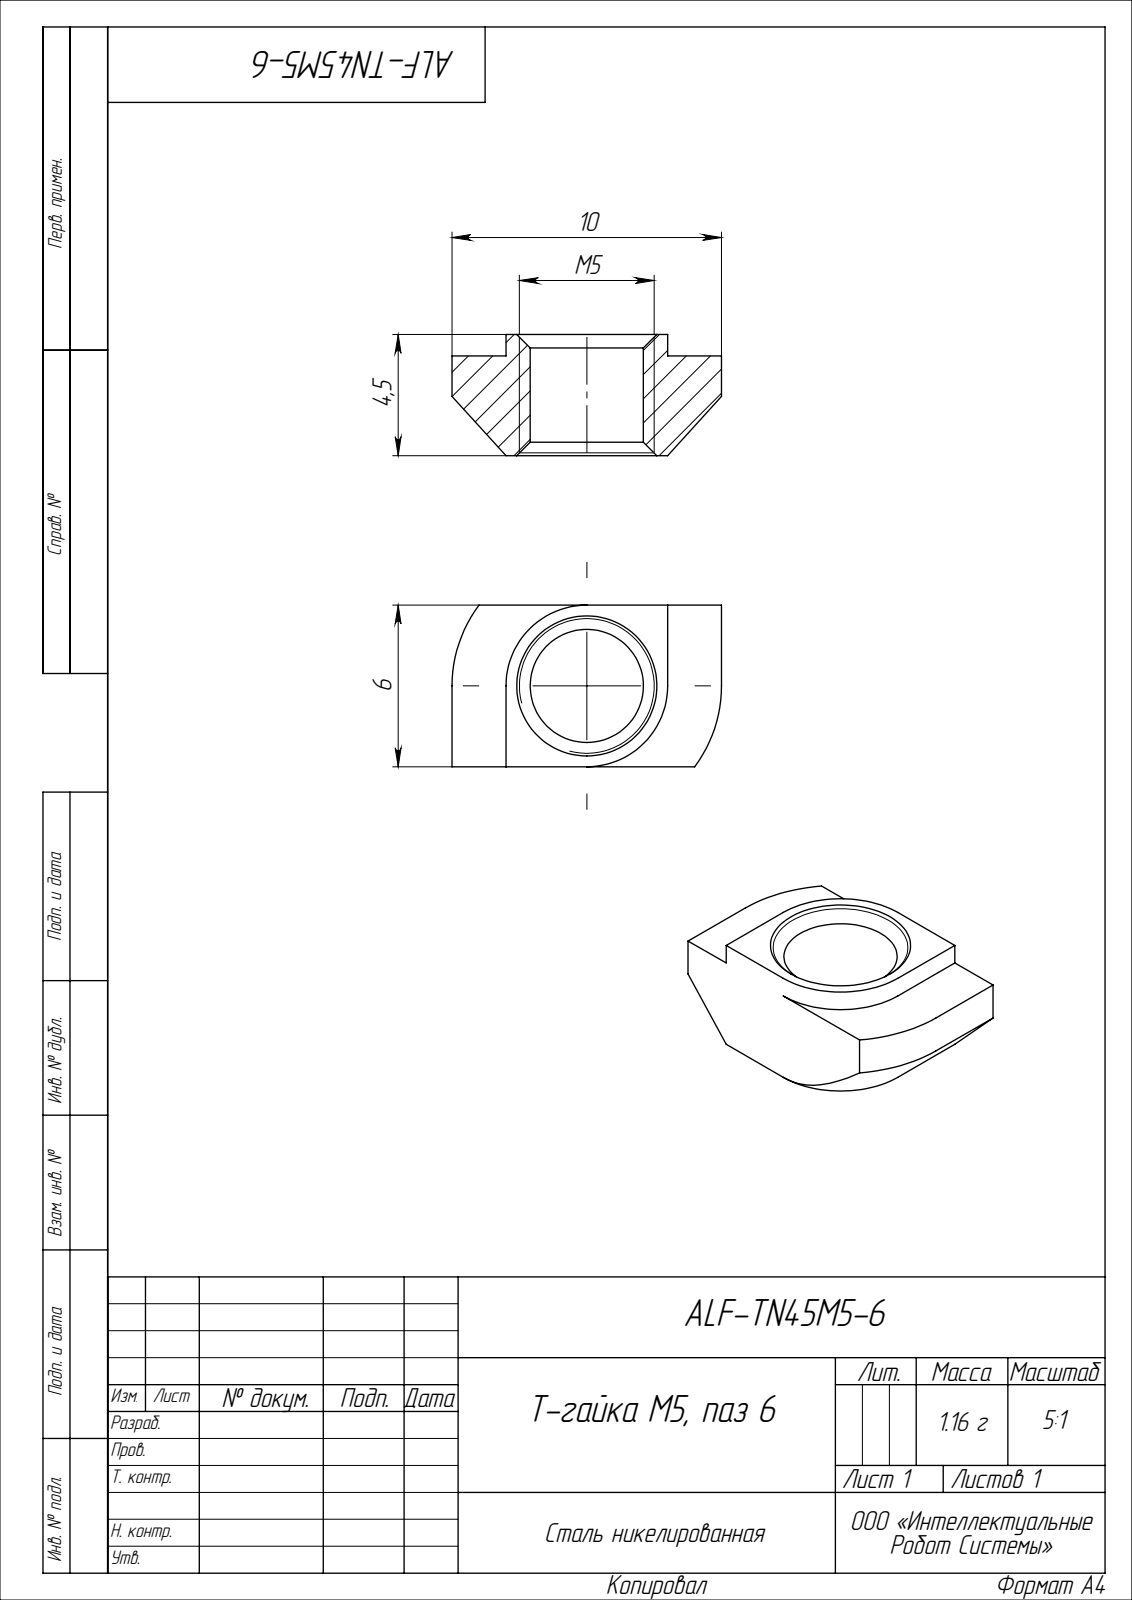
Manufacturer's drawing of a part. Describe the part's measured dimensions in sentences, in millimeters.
The part is named "ALF-TN45М5-6". Its 3-D file was written by "SolidWorks 2022 (CONFIG_CONTROL_DESIGN)". It is 1 solid with 24 faces: 12 planar, 6 cylindrical and 6 other. Overall it measures 10 by 6 by 4.5 millimeters. Its volume is 147 cubic millimeters and its surface area 245 square millimeters. Round holes: 1 of diameter 4.2. Partial cylindrical surfaces (rounded edges, fillets, slot ends): 1 of radius 3, 1 of radius 5. The main face-to-face distances are 6, 3.7, 4.5, 0.8, 2, 8, 10.
